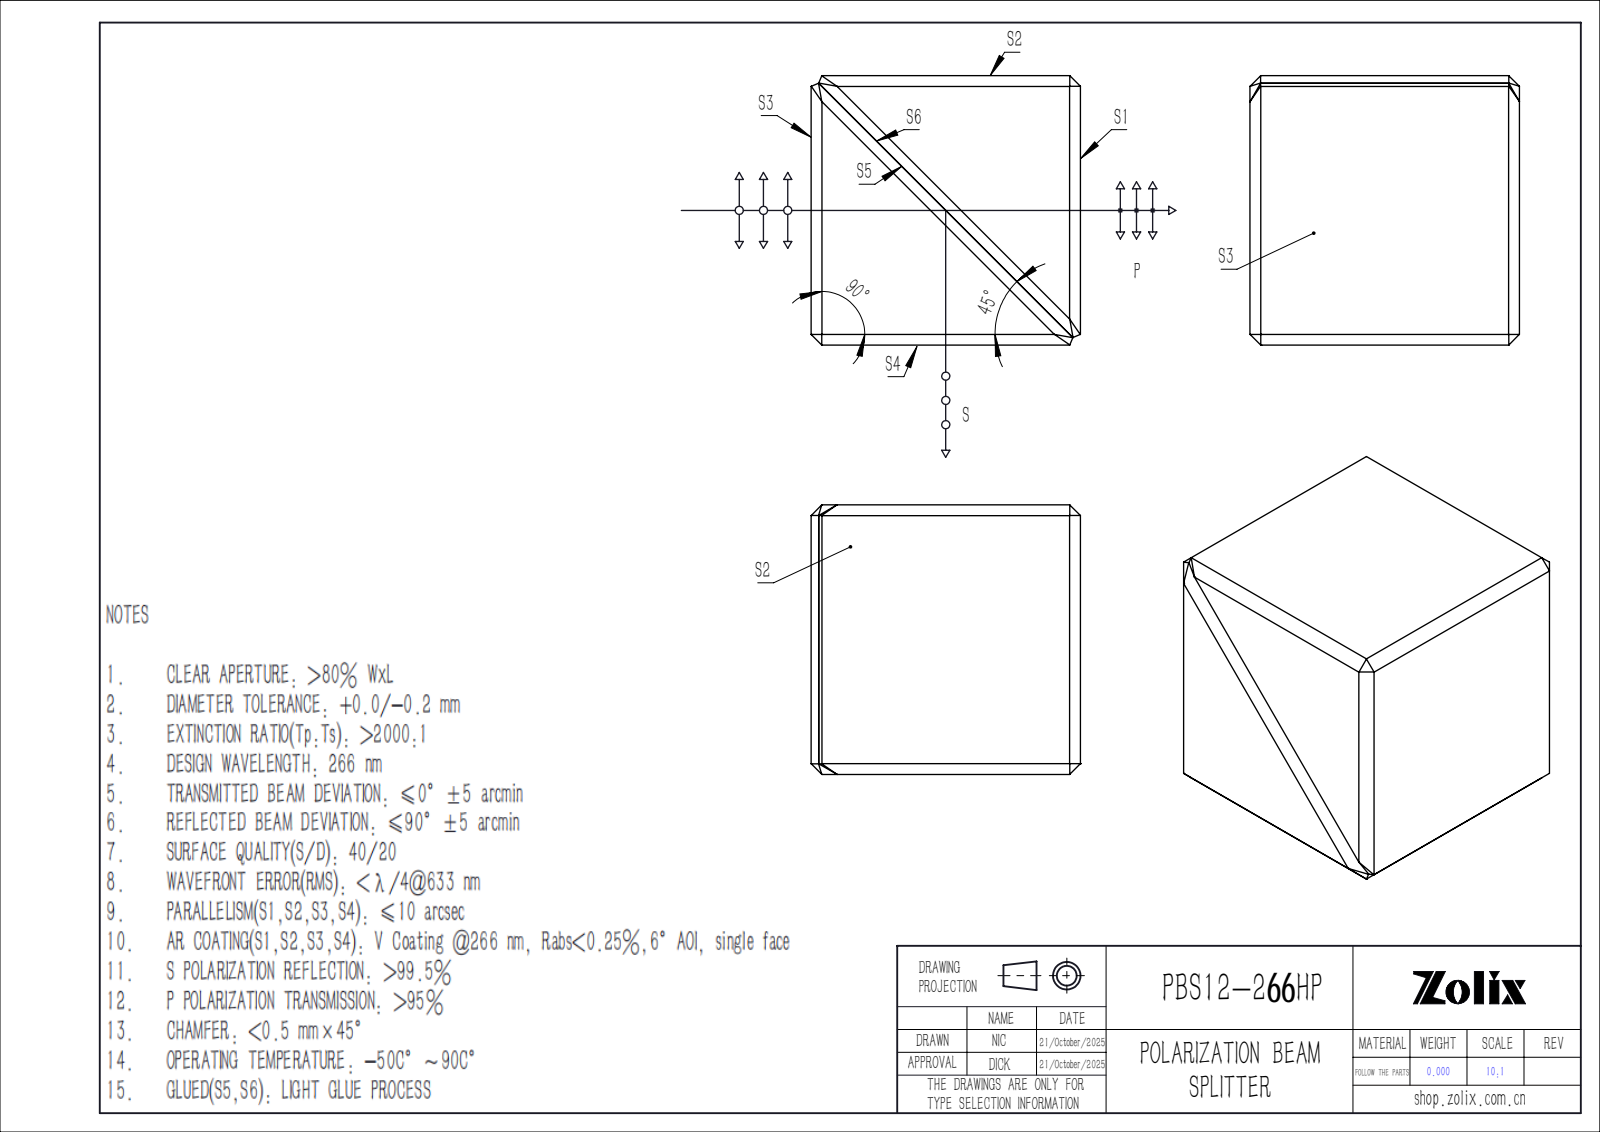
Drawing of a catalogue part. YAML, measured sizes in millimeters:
part_name: "PBS22-266-HP-1-1; PBS22-266-HP; PBS22-266-HP-1-2"
step_written_by: "SolidWorks 2022 (CONFIG_CONTROL_DESIGN)"
units: millimeters
bodies: {solids: 2, faces: 43, planar: 41, cylindrical: 2, other: 0}
overall_size: [12.7, 12.7, 12.7]
volume: 2044
surface_area: 1388
round_holes:
  - {diameter: 0.2, count: 1}
face_to_face_distances: [12.7, 17.67, 8.7, 17.68, 8.84, 8.83, 16.22, 16.23, 18.81, 21.52]
